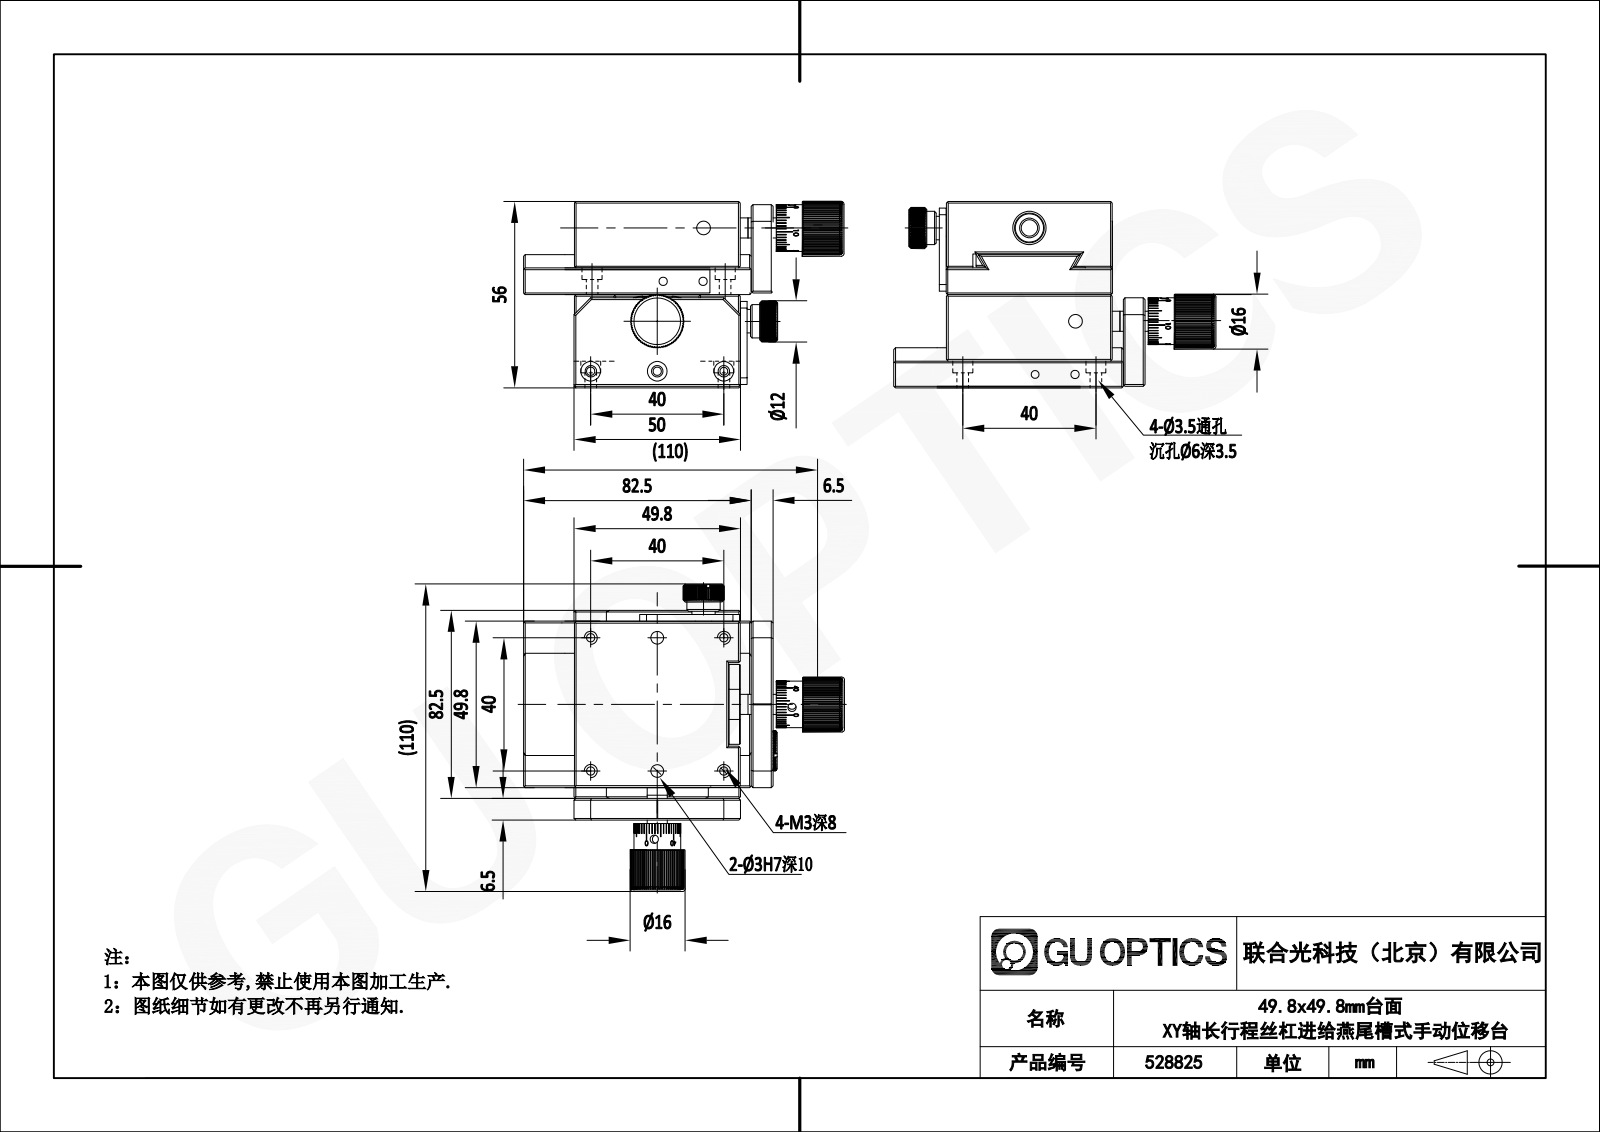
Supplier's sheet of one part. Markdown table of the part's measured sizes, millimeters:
| quantity | value |
| --- | --- |
| part name | 528825 |
| STEP written by | SolidWorks 2020 (CONFIG_CONTROL_DESIGN) |
| units | millimeters |
| bodies | 0 solids, 1360 faces (676 planar, 332 cylindrical, 352 other) |
| overall size | 110 × 110 × 56 |
| round holes (diameter × count) | 2.5 × 20, 2.05 × 12, 2.9 × 8, 3.4 × 8, 5 × 8, 3 × 6, 6 × 6, 1.5 × 4, 3.1 × 4, 6.5 × 4, 3.3 × 2, 3.5 × 2 |
| round bosses / shafts (diameter × count) | 3 × 10, 4.5 × 8, 2.5 × 8, 5.6 × 4, 5.5 × 4, 13 × 2, 12 × 2, 10.3 × 2 |
| partial cylindrical surfaces (radius × count) | 0.3 × 16, 2 × 8, 2.1 × 4, 7.5 × 2, 11.5 × 2 |
| main face-to-face distances | 28, 12, 16, 27.8, 4.5, 7.5, 20.5, 11.8, 7.3, 15.8 |
| hole center spacings | 8.5, 20, 44.72, 40, 13.6, 14.72, 15, 17 |
